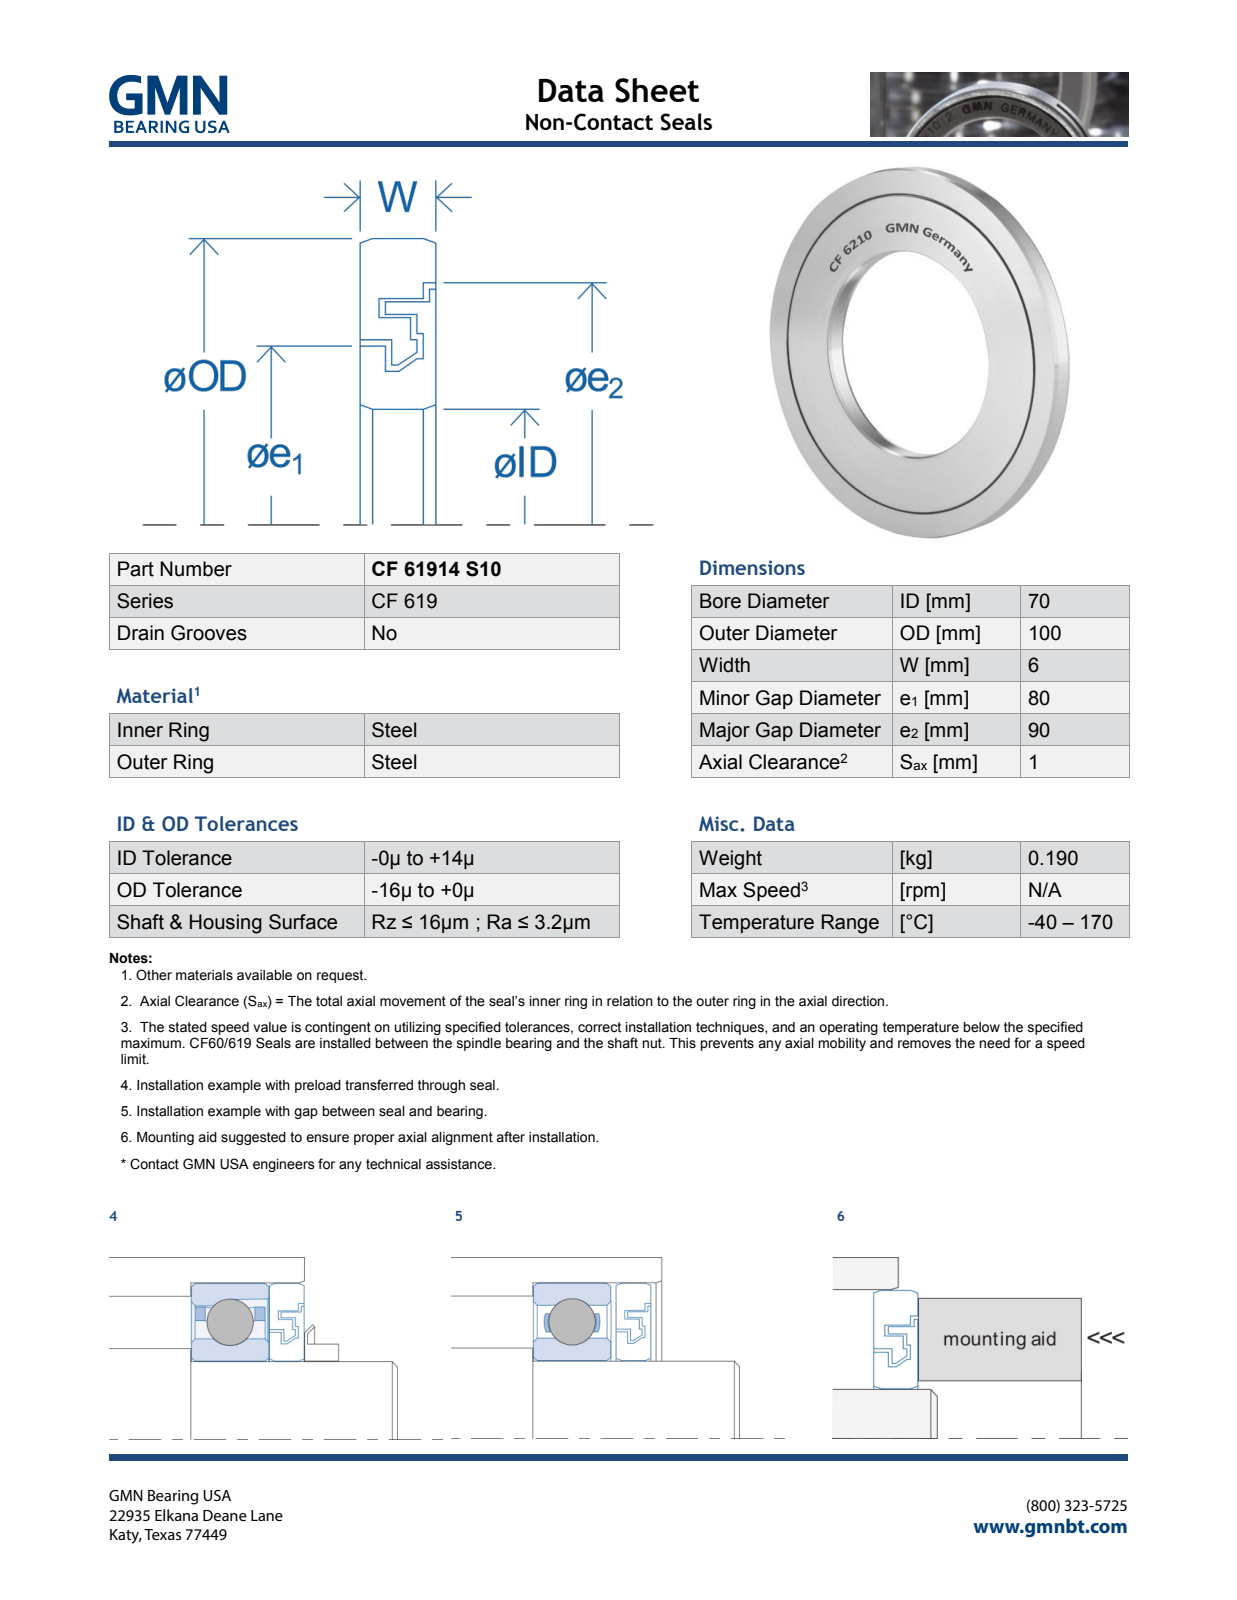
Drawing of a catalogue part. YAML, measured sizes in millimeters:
part_name: "CF61914S10_PRT"
step_written_by: "PRO/ENGINEER BY PARAMETRIC TECHNOLOGY CORPORATION, 2013150 (AUTOMOTIVE_DESIGN)"
units: millimeters
bodies: {solids: 2, faces: 647, planar: 605, cylindrical: 30, other: 12}
overall_size: [100, 100, 6.05]
volume: 21704
surface_area: 20956
round_holes:
  - {diameter: 70, count: 1}
  - {diameter: 77, count: 1}
  - {diameter: 81, count: 1}
  - {diameter: 82, count: 1}
  - {diameter: 85, count: 1}
  - {diameter: 87.5, count: 1}
  - {diameter: 90, count: 1}
round_bosses_or_shafts:
  - {diameter: 100, count: 1}
  - {diameter: 89, count: 1}
  - {diameter: 87, count: 1}
  - {diameter: 84.5, count: 1}
  - {diameter: 80, count: 1}
  - {diameter: 78, count: 1}
  - {diameter: 76, count: 1}
face_to_face_distances: [6, 0.5, 2, 2.5, 1, 1.5, 4, 3, 3.5, 4.5]
